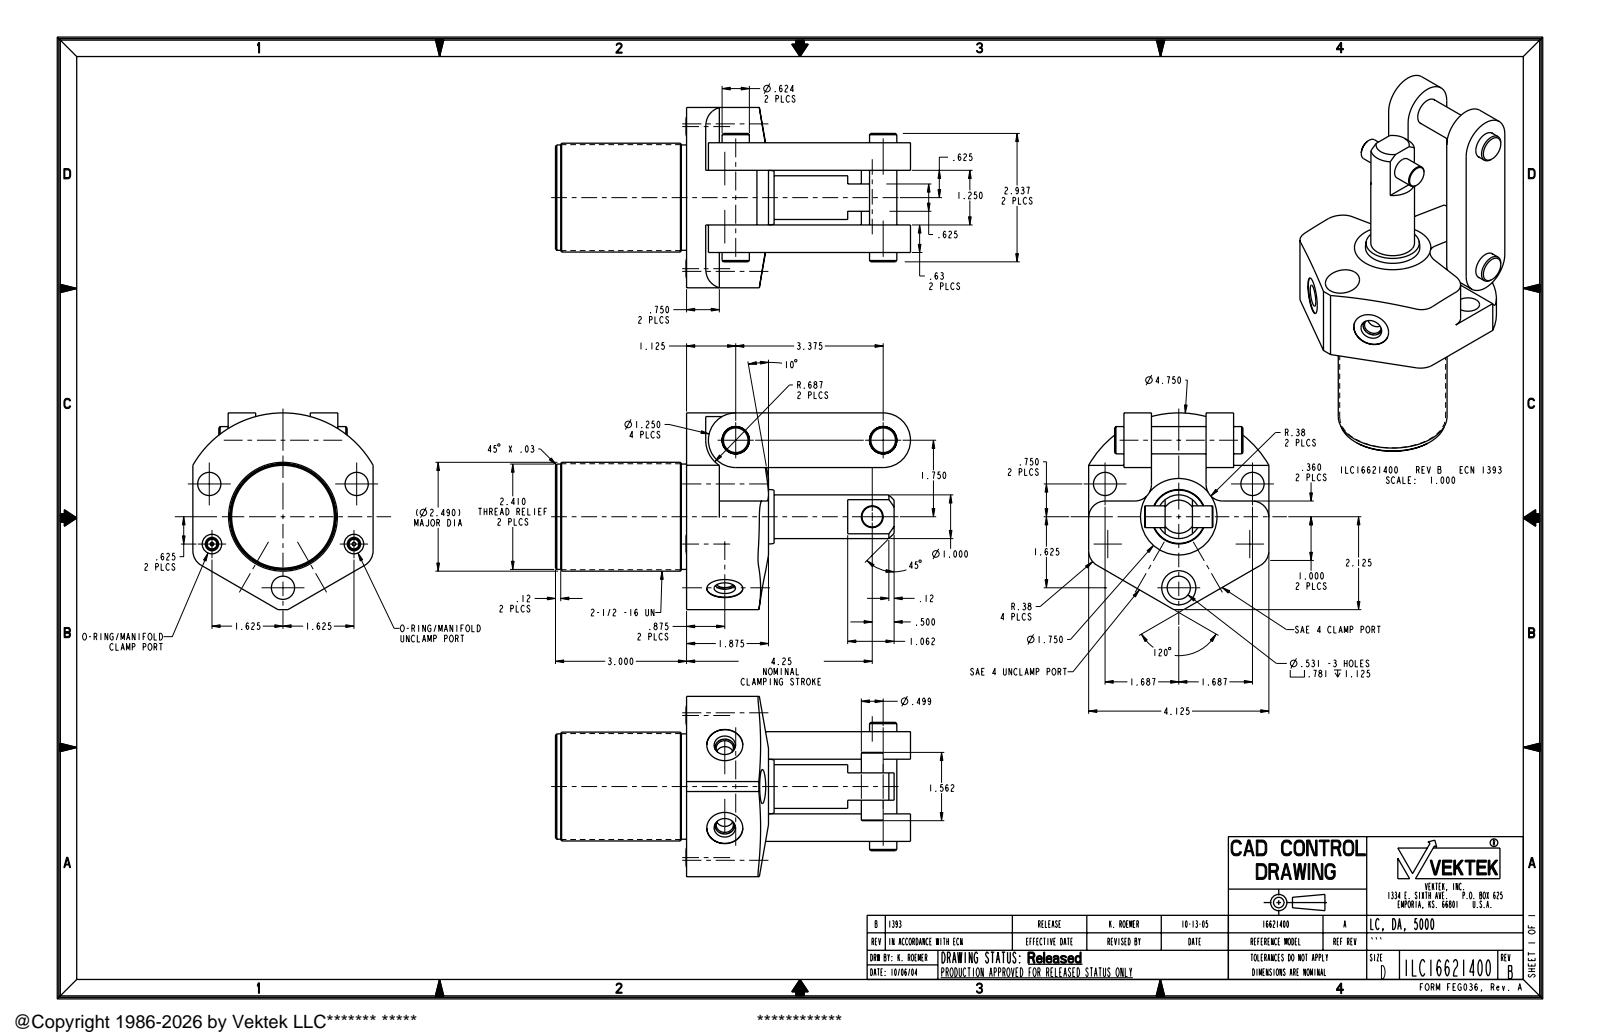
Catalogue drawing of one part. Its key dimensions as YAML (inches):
part_name: "ILC16621400"
step_written_by: "PRO/ENGINEER BY PARAMETRIC TECHNOLOGY CORPORATION, 2004290 (AUTOMOTIVE_DESIGN_CC2)"
units: inches
bodies: {solids: 1, faces: 298, planar: 119, cylindrical: 131, other: 48}
overall_size: [8.125, 4.5, 4.125]
volume: 44.55
surface_area: 154.1
round_holes:
  - {diameter: 0.047, count: 6}
  - {diameter: 0.531, count: 3}
  - {diameter: 0.098, count: 2}
  - {diameter: 0.256, count: 2}
  - {diameter: 0.392, count: 2}
  - {diameter: 0.447, count: 2}
  - {diameter: 0.825, count: 2}
  - {diameter: 0.781, count: 1}
round_bosses_or_shafts:
  - {diameter: 0.715, count: 2}
  - {diameter: 0.625, count: 2}
  - {diameter: 0.437, count: 2}
  - {diameter: 0.224, count: 2}
  - {diameter: 0.118, count: 2}
  - {diameter: 2.49, count: 1}
  - {diameter: 2.424, count: 1}
  - {diameter: 2.41, count: 1}
partial_cylinders:
  - {radius: 0.047, count: 12}
  - {radius: 0.38, count: 6}
  - {radius: 0.625, count: 2}
  - {radius: 0.687, count: 1}
  - {radius: 2.375, count: 1}
face_to_face_distances: [0.625, 1.875, 2.5, 1.25, 3, 0.813, 1.437, 2.688, 3.313, 1.25]
hole_center_spacings: [0.113, 1.377, 1.76, 1.907, 2.913, 3.375, 3.377, 3.586]
